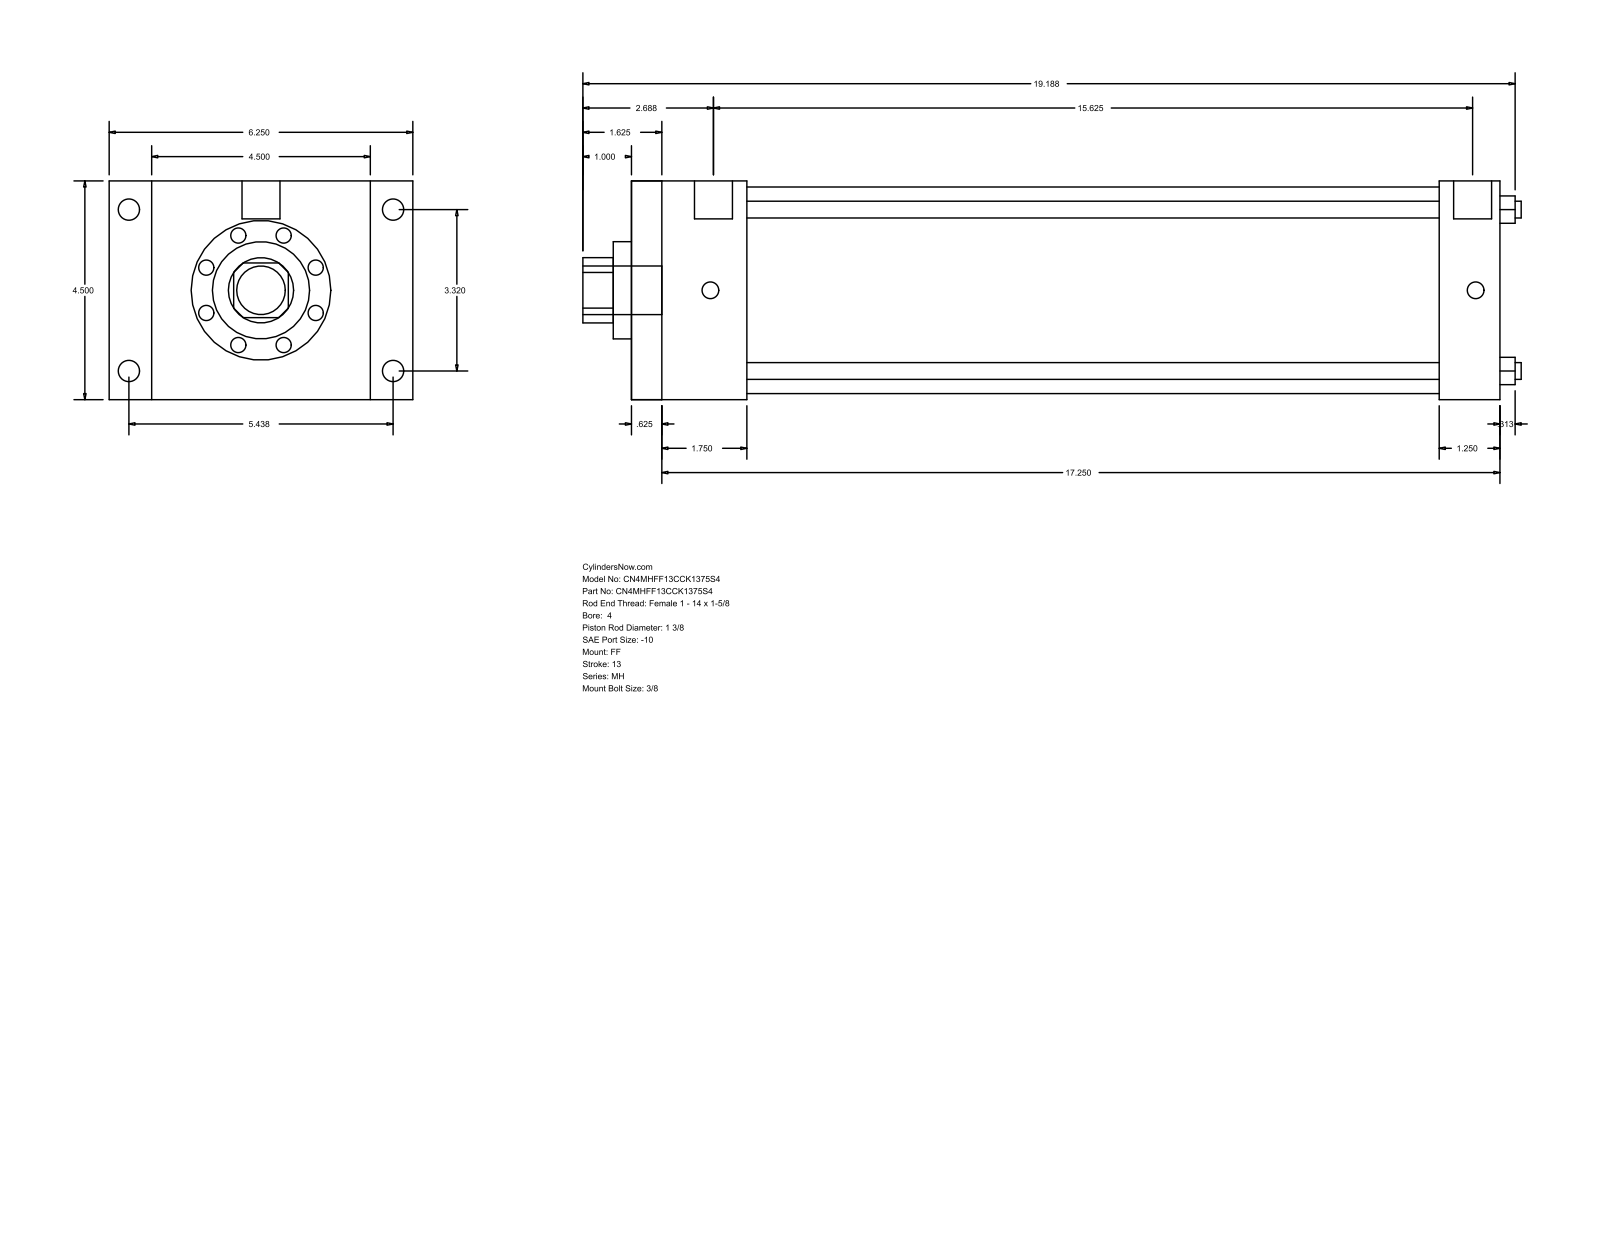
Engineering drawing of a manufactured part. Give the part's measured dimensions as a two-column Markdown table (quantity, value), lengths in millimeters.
| quantity | value |
| --- | --- |
| part name | MH_FF__0400_1.375 |
| STEP written by | GSSL Pune (CONFIG_CONTROL_DESIGN) |
| units | millimeters |
| bodies | 0 solids, 92 faces (64 planar, 28 cylindrical, 0 other) |
| overall size | 490.54 × 158.75 × 114.3 |
| round holes (diameter × count) | 8.76 × 4, 34.92 × 1, 50.8 × 1, 107.95 × 1 |
| round bosses / shafts (diameter × count) | 11.13 × 4, 8.73 × 4, 19.84 × 2, 25.4 × 1 |
| partial cylindrical surfaces (radius × count) | 17.06 × 1 |
| main face-to-face distances | 114.3, 454.03, 15.87, 438.16, 60.32, 44.45, 393.71, 422.28, 406.41, 361.96 |
| hole center spacings | 59.62, 84.32, 119.25 |
